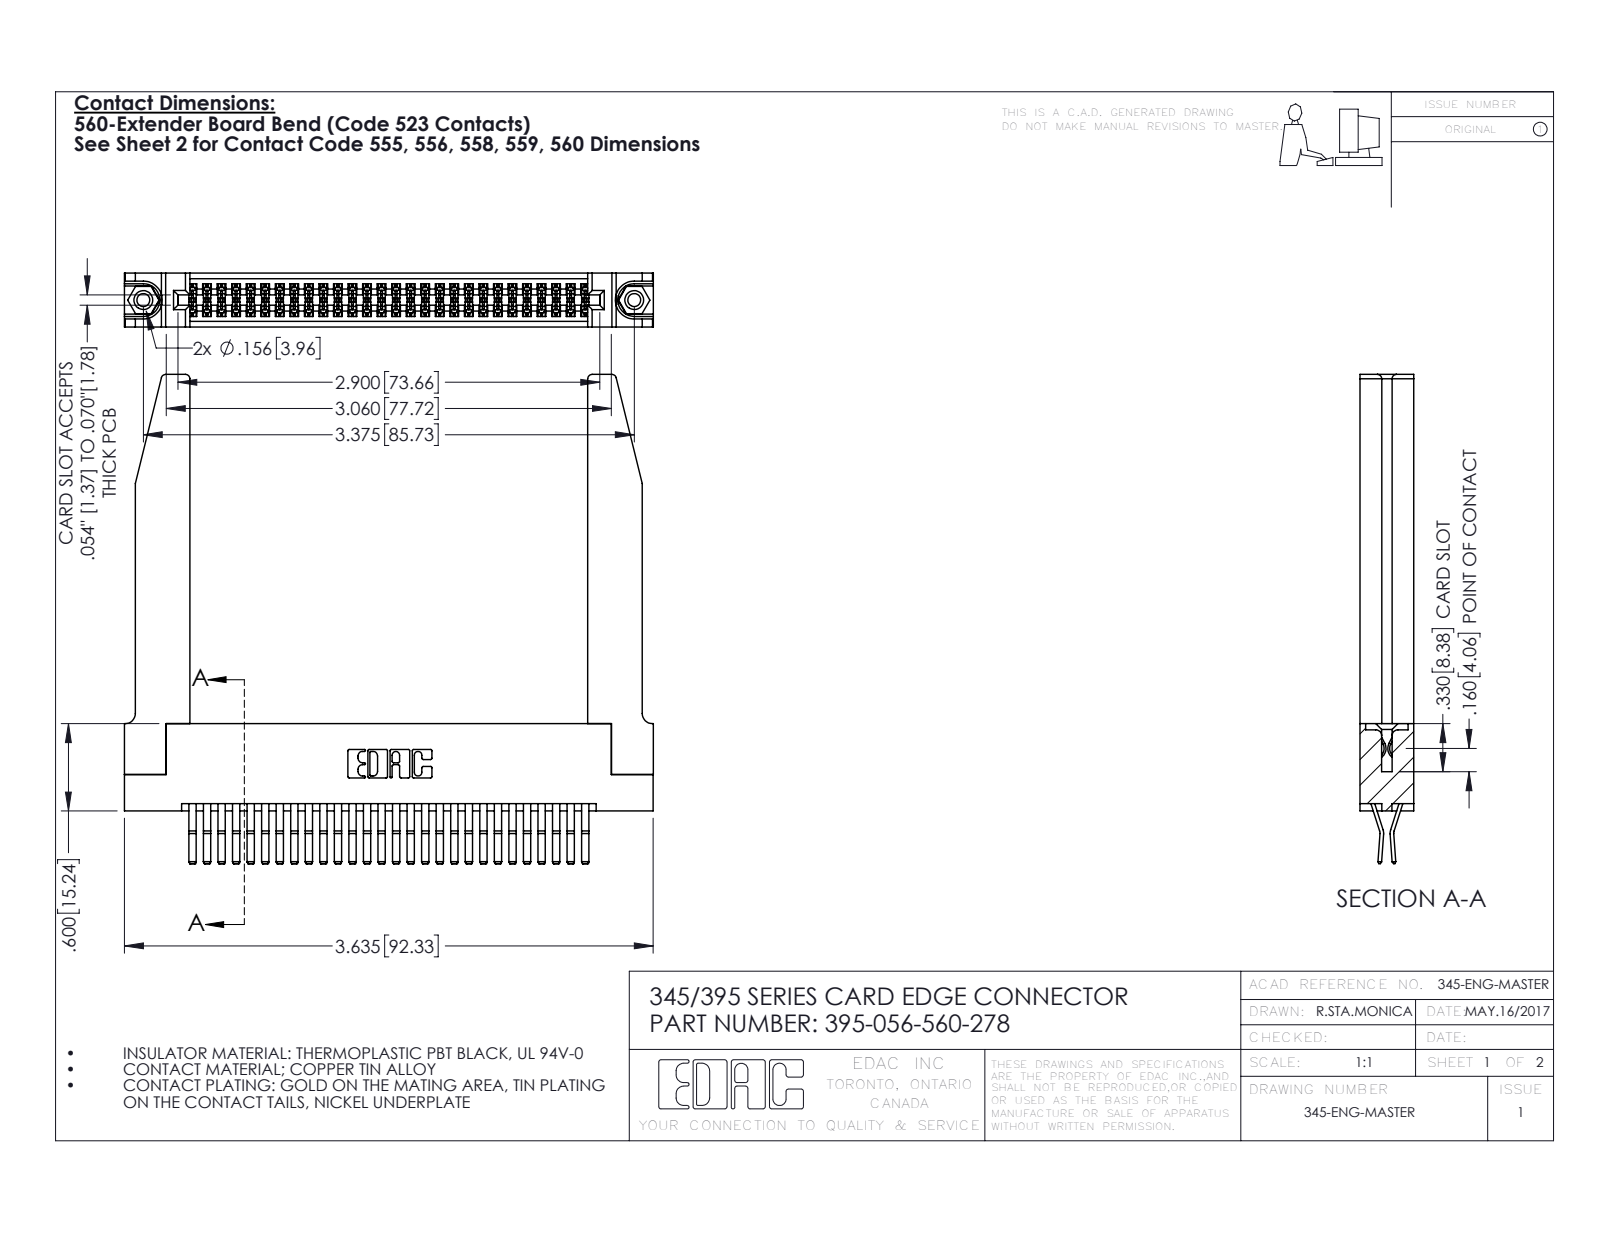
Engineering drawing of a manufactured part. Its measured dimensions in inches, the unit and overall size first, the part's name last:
Units: inches
Overall size (bounding box): 3.636 × 3.362 × 0.37
Round holes (diameter × count): ⌀0.089 ×2, ⌀0.125 ×2, ⌀0.156 ×2, ⌀0.064 ×1
Round bosses / shafts (diameter × count): ⌀0.155 ×2
Partial cylindrical surfaces — rounded edges, fillets, slot ends (radius × count): R0.006 ×111, R0.01 ×22, R0.03 ×8, R0.007 ×6, R0.031 ×6, R0.026 ×3, R0.01 ×2, R0.014 ×2
Main face-to-face distances: 0.37, 0.072, 0.298, 0.025, 0.2, 0.098, 0.272, 0.225, 0.148, 0.15
Hole centre spacings: 0.27, 3.14, 3.375
Volume: 1.036 in³ · Surface area: 32.74 in²
Bodies: 61 solids, 3272 faces (2070 planar, 1150 cylindrical, 52 other)
Part name (STEP PRODUCT): 395-056-560-278; 345-292-001_560 Tail; 345 Part_Flush Mounting Lugs - 0.156 Dia-TH; 345-220-078_345-220-078 (+1 more)
STEP written by: SolidWorks 2016 (CONFIG_CONTROL_DESIGN)
